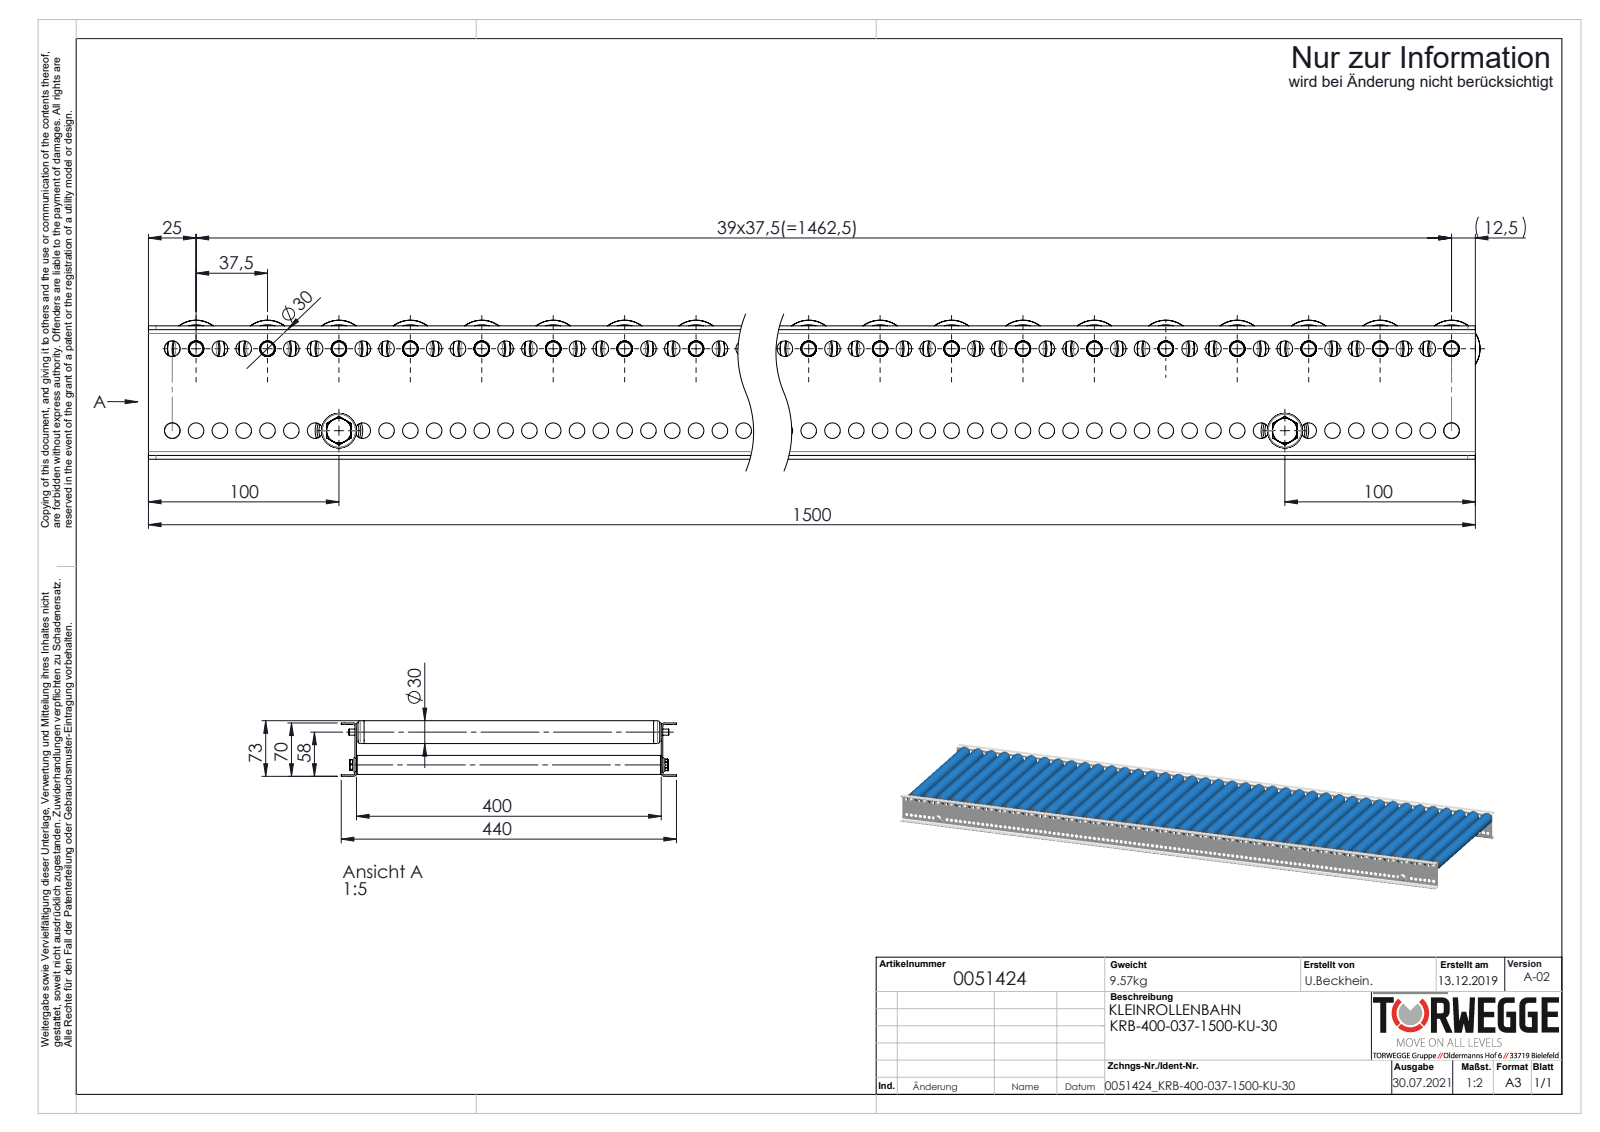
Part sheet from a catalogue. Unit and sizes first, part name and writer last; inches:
Units: inches
Overall size (bounding box): 59.154 × 17.323 × 2.874
Round holes (diameter × count): ⌀0.323 ×238, ⌀0.319 ×40, ⌀0.89 ×40, ⌀0.992 ×40, ⌀0.268 ×2, ⌀0.827 ×2
Round bosses / shafts (diameter × count): ⌀0.315 ×42, ⌀1.181 ×40, ⌀1.177 ×40, ⌀1.043 ×40, ⌀1.039 ×40, ⌀0.945 ×40, ⌀0.984 ×2
Partial cylindrical surfaces — rounded edges, fillets, slot ends (radius × count): R0.199 ×40, R0.157 ×8, R0.079 ×4
Main face-to-face distances: 0.079, 15.827, 15.748, 2.677, 15.906, 2.756, 2.598, 0.394, 15.354, 0.472
Hole centre spacings: 0.492, 0.984, 1.476, 1.969, 2.461, 2.953, 3.445, 3.937
Volume: 243 in³ · Surface area: 6 718 in²
Bodies: 92 solids, 9472 faces (2920 planar, 3568 cylindrical, 2984 other)
Part name (STEP PRODUCT): Traversen_KFG_L400; S100995_TYP-KUT50-30x1,8-A8; 0051424; KUT50-30x1,8-KB-A8-FA_KFG_0034506TWG_KUT50-30x1,8-KB-A8-FA-EL=400 (+4 more)
STEP written by: SolidWorks 2020 (AUTOMOTIVE_DESIGN)
